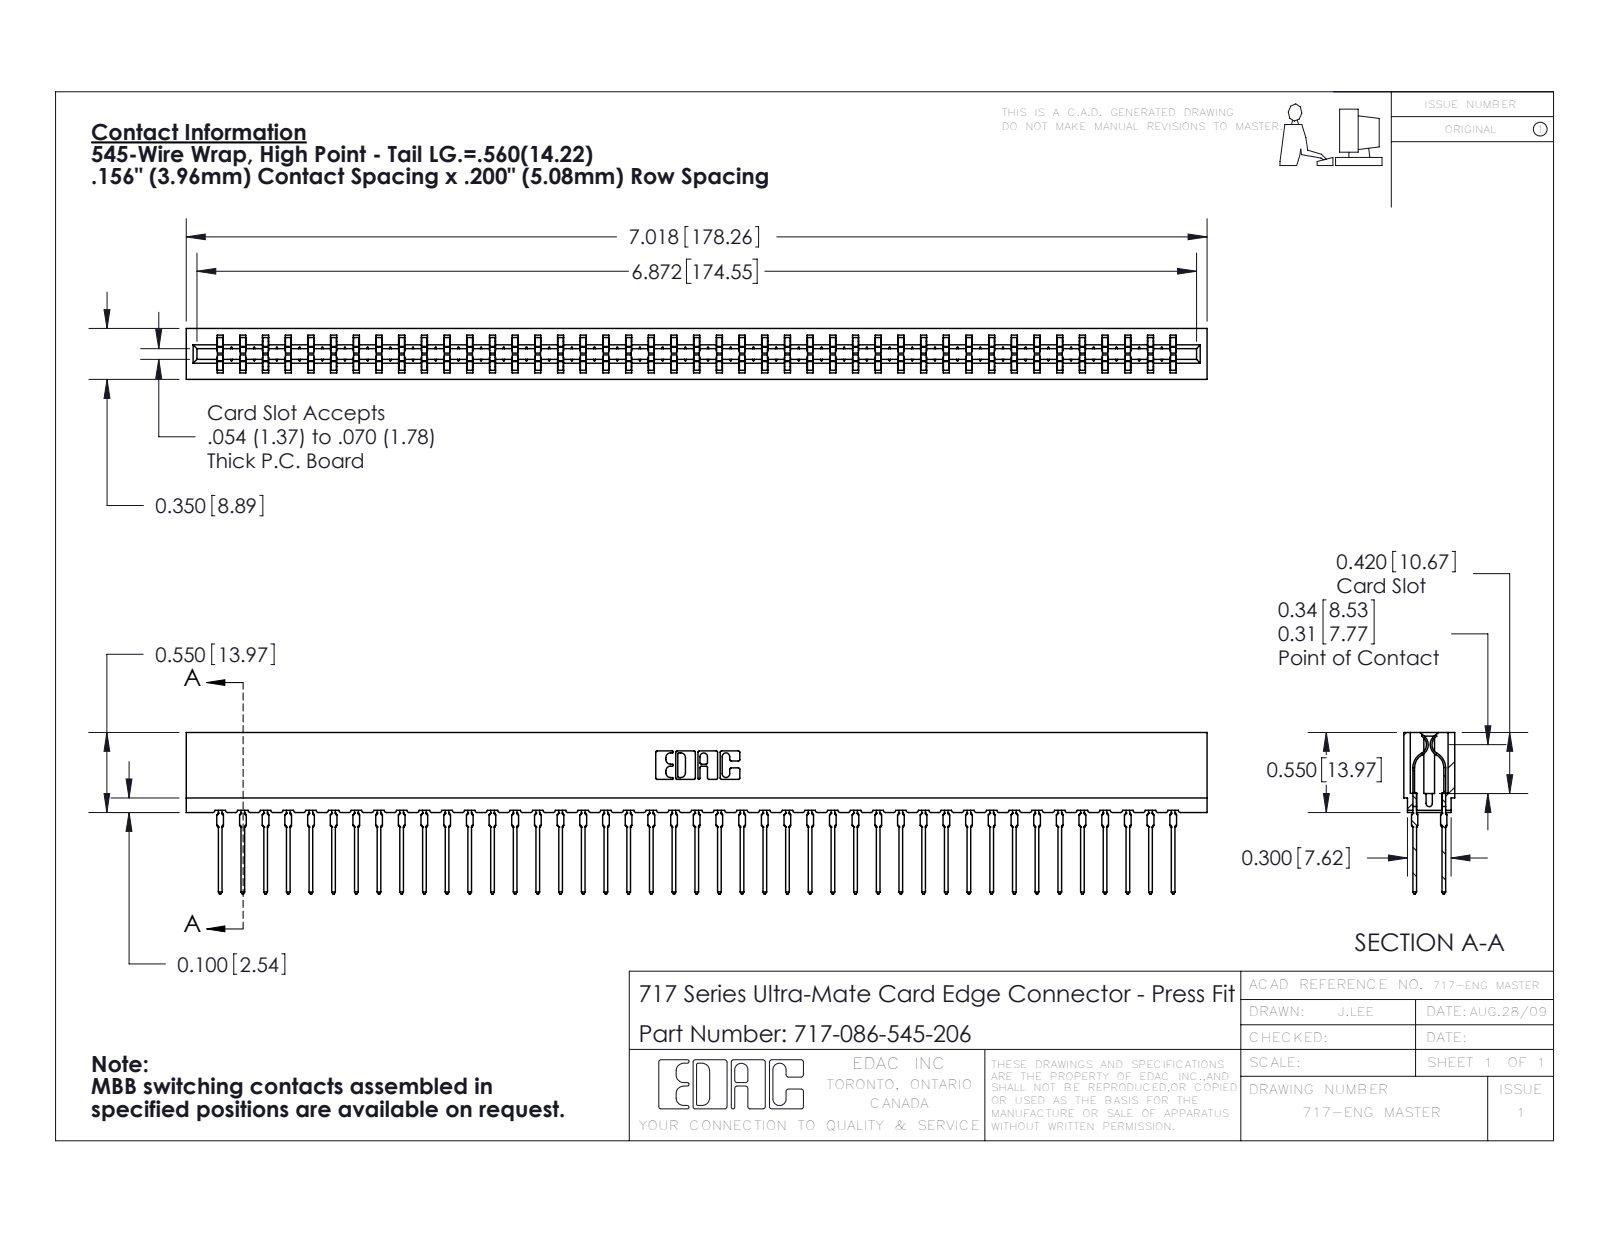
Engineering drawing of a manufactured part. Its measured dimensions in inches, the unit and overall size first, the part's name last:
Units: inches
Overall size (bounding box): 7.018 × 1.109 × 0.35
Partial cylindrical surfaces — rounded edges, fillets, slot ends (radius × count): R0.021 ×172, R0.015 ×86, R0.01 ×22, R0.005 ×8, R0.011 ×8, R0.007 ×6, R0.031 ×6, R0.026 ×3
Main face-to-face distances: 0.212, 0.138, 0.35, 0.063, 0.287, 0.076, 0.149, 0.074, 0.087, 0.263
Volume: 0.961 in³ · Surface area: 39.61 in²
Bodies: 87 solids, 7834 faces (4053 planar, 1545 cylindrical, 2236 other)
Part name (STEP PRODUCT): 745-292-001_545; 717-086-545-206; 717 Part_Insulator Option - 06
STEP written by: SolidWorks 2016 (CONFIG_CONTROL_DESIGN)
